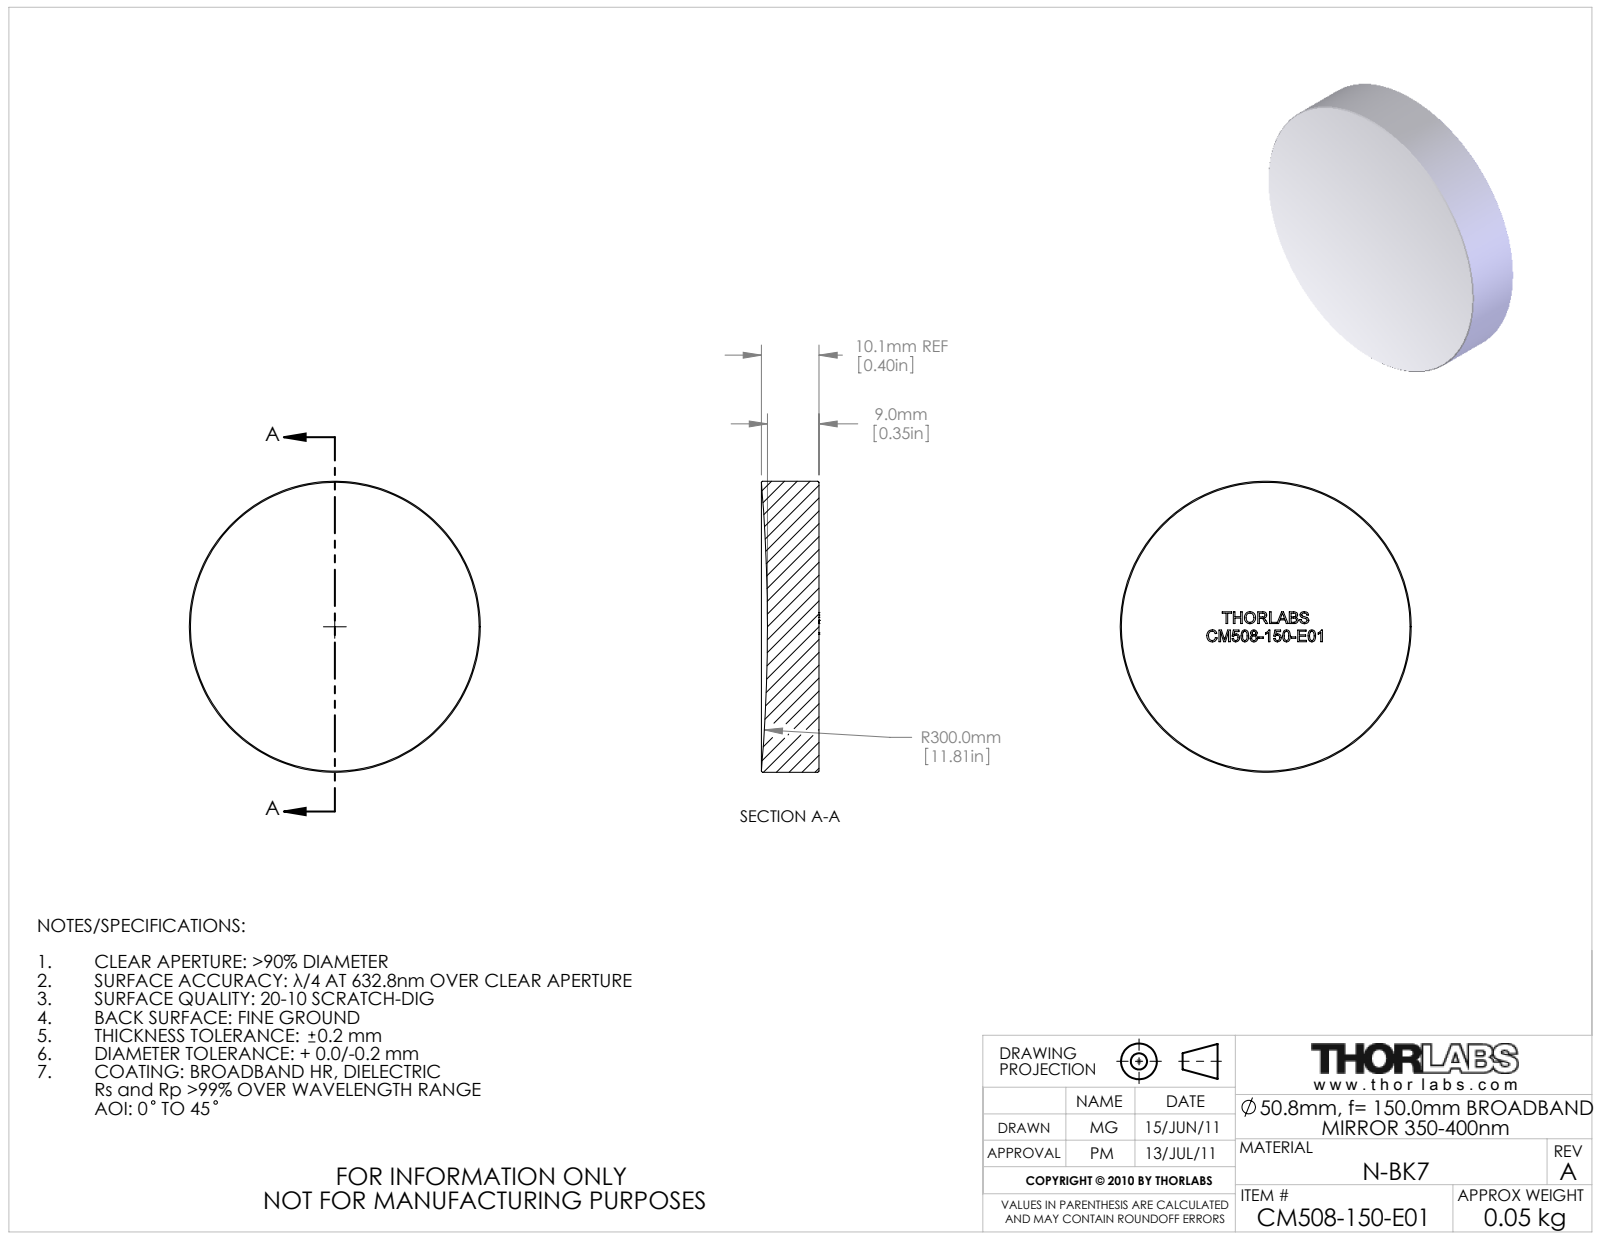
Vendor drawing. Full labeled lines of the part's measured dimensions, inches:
Part name (STEP PRODUCT): 22617-E0W
STEP written by: SolidWorks 2011 (AUTOMOTIVE_DESIGN)
Units: inches
Bodies: 0 solids, 44 faces (34 planar, 2 cylindrical, 8 other)
Overall size (bounding box): 2 × 2 × 0.396
Round bosses / shafts (diameter × count): ⌀2 ×1
